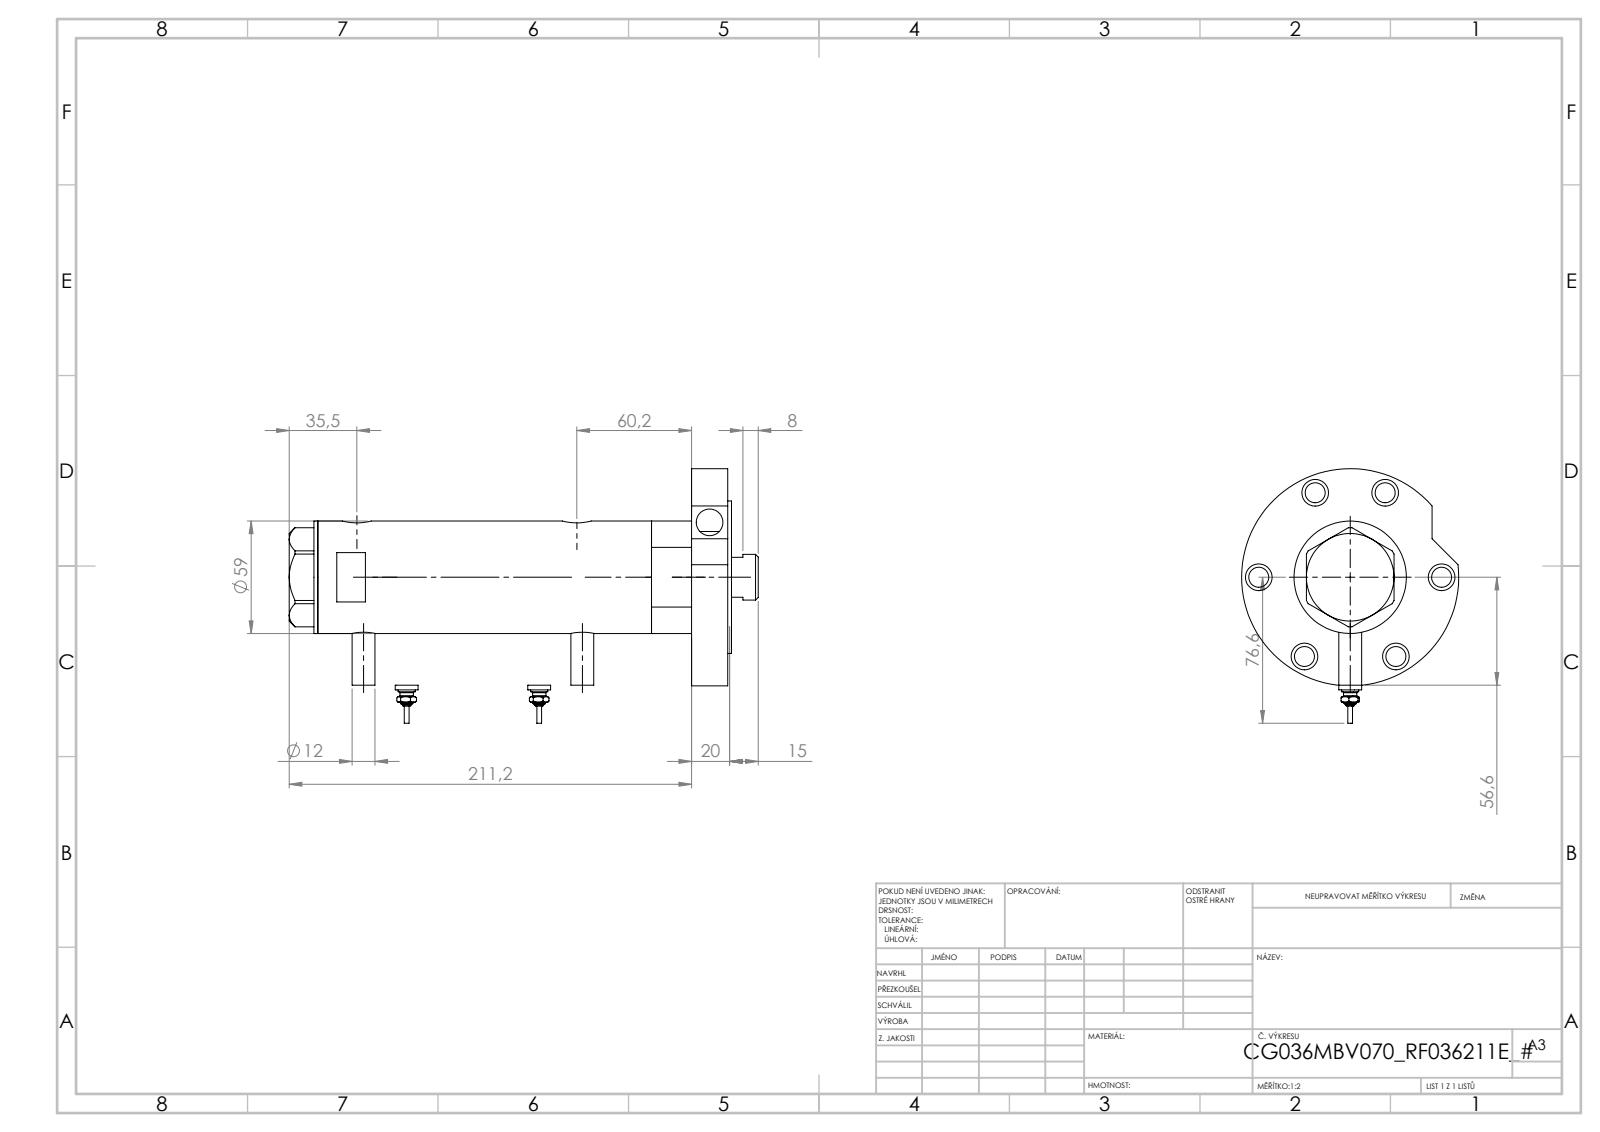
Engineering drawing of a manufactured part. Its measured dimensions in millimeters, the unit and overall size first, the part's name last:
Units: millimetres
Overall size (bounding box): 233.42 × 118.8 × 114
Round holes (diameter × count): ⌀14 ×7, ⌀10.5 ×6, ⌀5 ×2, ⌀9.73 ×2, ⌀12.5 ×2, ⌀15 ×2, ⌀8.5 ×1, ⌀25 ×1, ⌀26.5 ×1, ⌀36 ×1, ⌀40 ×1, ⌀48 ×1
Round bosses / shafts (diameter × count): ⌀12 ×4, ⌀9 ×2, ⌀7 ×2, ⌀4.34 ×2, ⌀2.4 ×2, ⌀114 ×1, ⌀80 ×1, ⌀59 ×1
Main face-to-face distances: 19, 2, 201.84, 21, 180.84, 199.84, 127.34, 53.5, 72.5, 74.5
Hole centre spacings: 48, 2.9, 3.5, 53.34, 79.82, 83.14, 86.1, 95.8
Volume: 664 668 mm³ · Surface area: 143 701 mm²
Bodies: 7 solids, 276 faces (92 planar, 110 cylindrical, 74 other)
Part name (STEP PRODUCT): V270CG_BACK; V270CG_SWITCH; V270CG_VC; V270CG_RF211E (+2 more)
STEP written by: SolidWorks 2019 (CONFIG_CONTROL_DESIGN)
